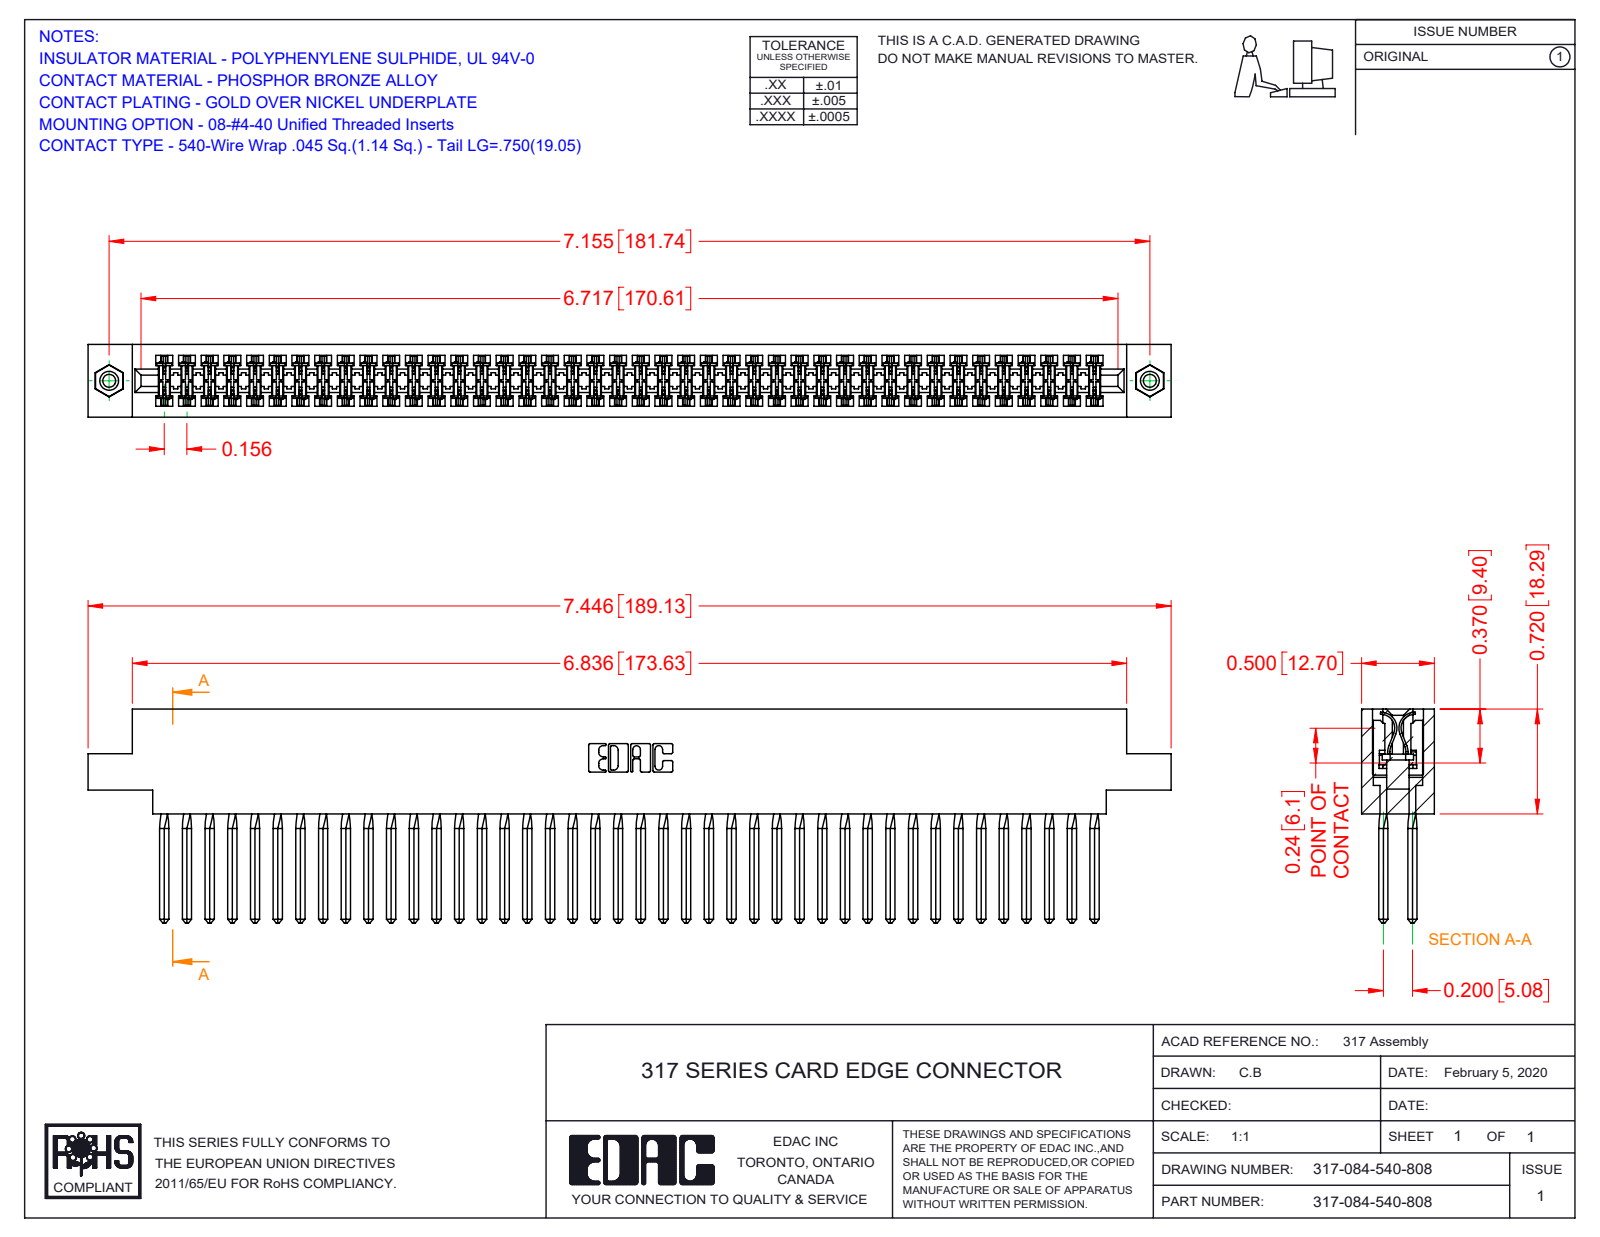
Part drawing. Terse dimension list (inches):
name: 317 Part_.156 Dia - TI; 345-250-001_345-250-003-102; 317-290-001_540; 317-084-540-878
written by: SolidWorks 2016 (CONFIG_CONTROL_DESIGN)
unit: in
bodies: 87 solids, 7638 faces (6222 planar, 1064 cylindrical, 352 other)
size: 7.446 × 1.47 × 0.5
volume: 1.937 in³; area: 73.37 in²
holes: 2× ⌀0.089, 2× ⌀0.125, 2× ⌀0.156
bosses: 2× ⌀0.155
rounds: 168× R0.015, 22× R0.01, 6× R0.007, 6× R0.031, 3× R0.026, 2× R0.095, 2× R0.1, 2× R0.11
face distances: 0.5, 0.075, 0.425, 0.35, 0.195, 0.094, 0.2, 0.115, 0.131, 0.046
hole spacings: 7.155
